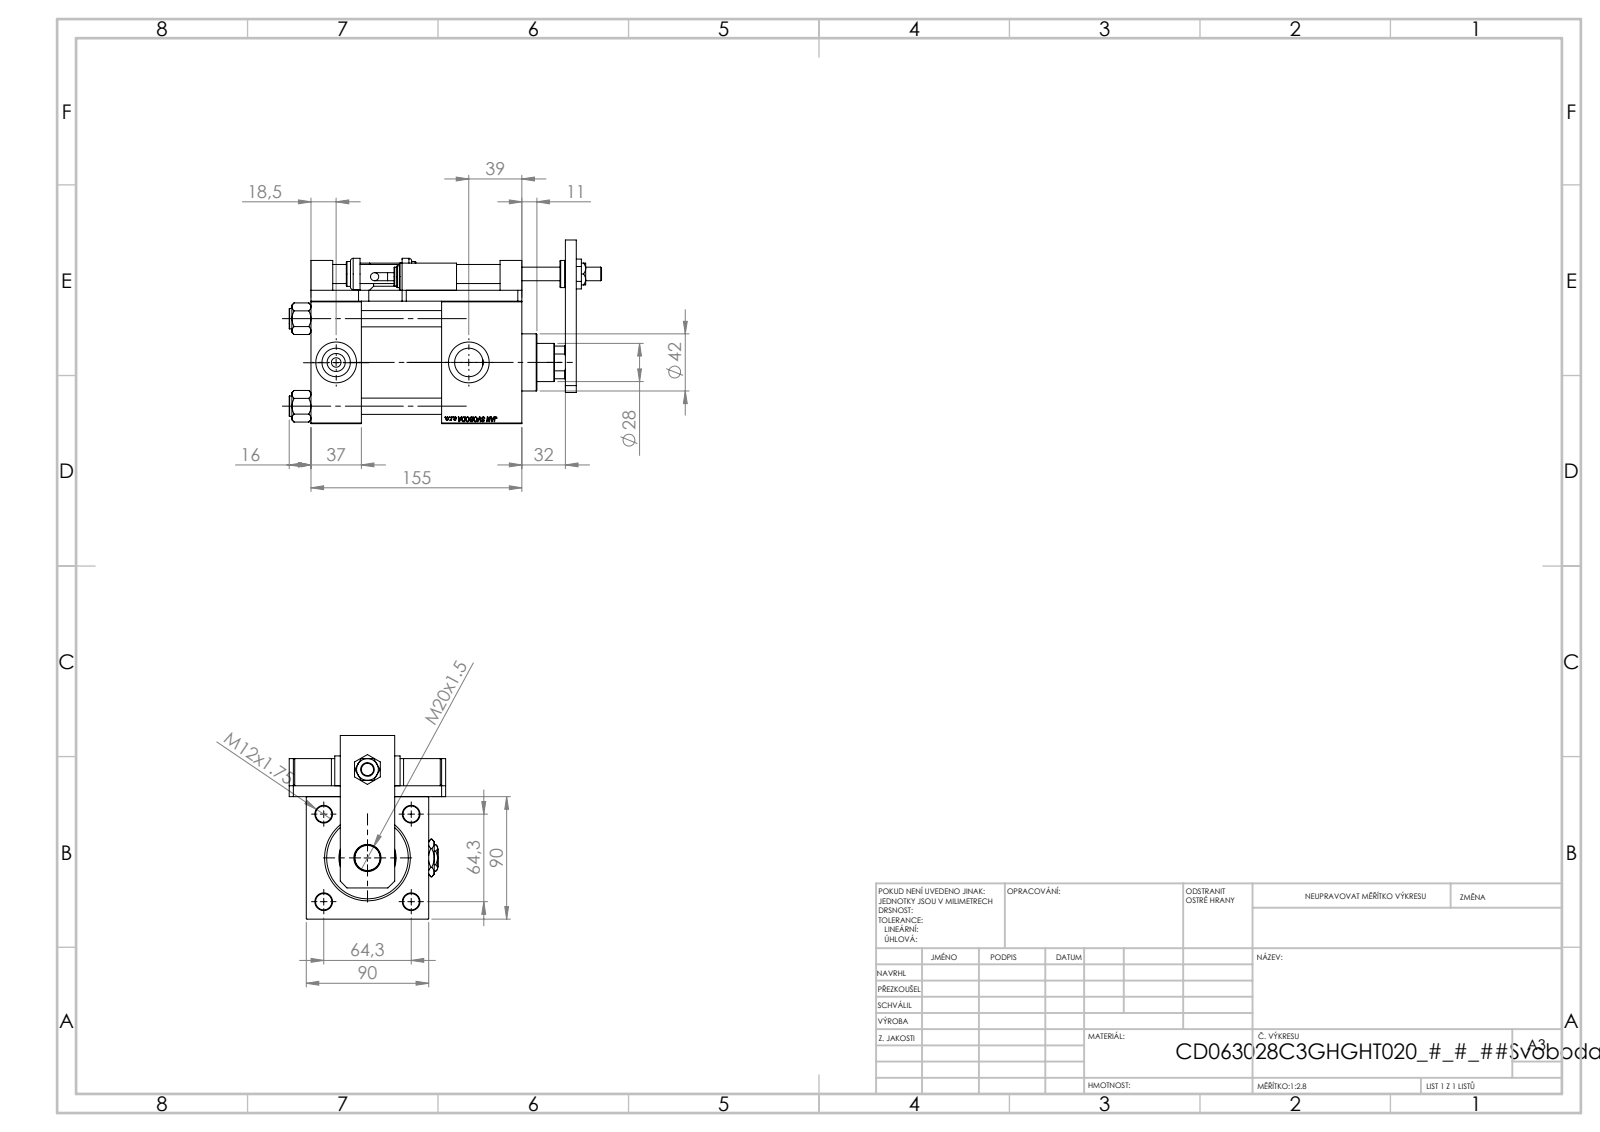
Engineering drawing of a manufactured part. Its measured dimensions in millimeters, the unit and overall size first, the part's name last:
Units: millimetres
Overall size (bounding box): 229.5 × 135 × 115
Round holes (diameter × count): ⌀8.5 ×4, ⌀12 ×4, ⌀13.5 ×4, ⌀7 ×2, ⌀20.96 ×2, ⌀30 ×2, ⌀10 ×1, ⌀14 ×1, ⌀18.5 ×1, ⌀20 ×1, ⌀28 ×1, ⌀31 ×1
Round bosses / shafts (diameter × count): ⌀15 ×4, ⌀20 ×3, ⌀16 ×2, ⌀14 ×2, ⌀6 ×2, ⌀69 ×1, ⌀42 ×1, ⌀23 ×1
Partial cylindrical surfaces — rounded edges, fillets, slot ends (radius × count): R7.5 ×4, R13.5 ×1
Main face-to-face distances: 8, 90, 118, 59, 37, 98, 155, 20, 32, 40
Hole centre spacings: 45.47, 64.3, 32, 45.96, 90.93, 102.33, 139, 142.64
Volume: 1 206 000 mm³ · Surface area: 269 156 mm²
Bodies: 26 solids, 1478 faces (695 planar, 166 cylindrical, 617 other)
Part name (STEP PRODUCT): V215CD_SWITCH_Q_BLOK; V215CD_SWITCH_Q_PODLOZKA_BACK; V215CD_SWITCH_Q_NUT10; V215CD_VC_C (+8 more)
STEP written by: SolidWorks 2019 (CONFIG_CONTROL_DESIGN)
